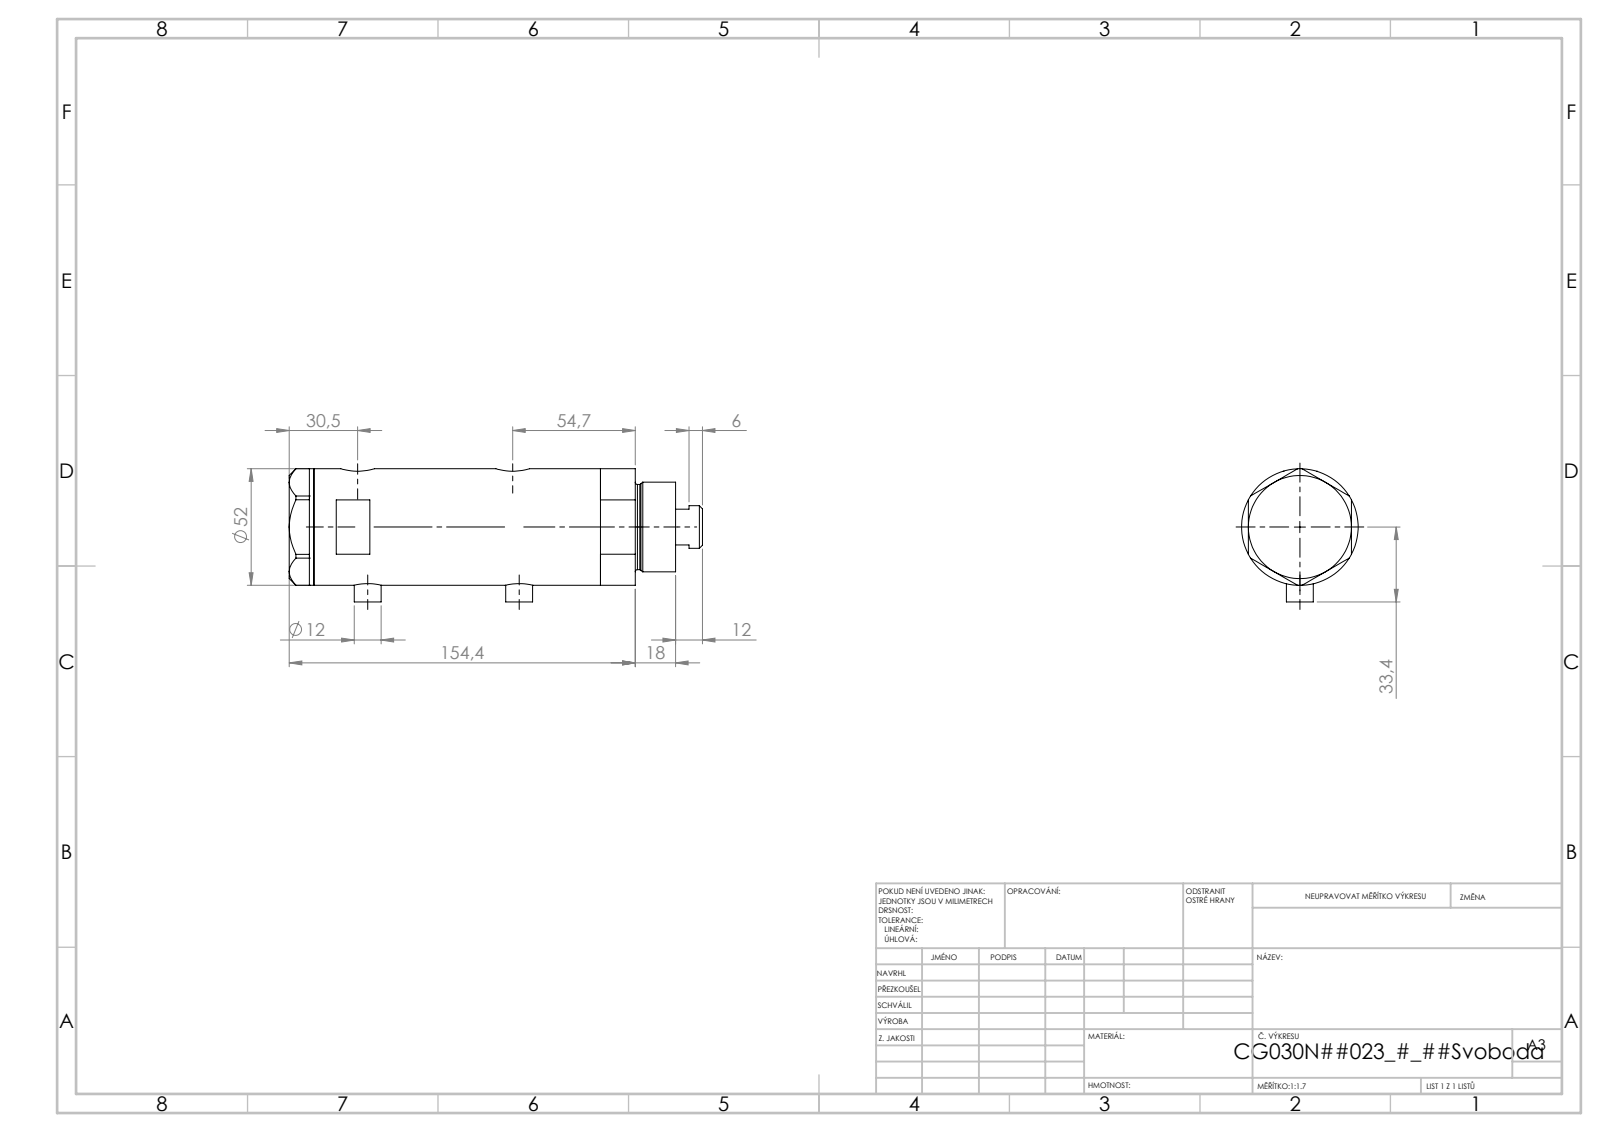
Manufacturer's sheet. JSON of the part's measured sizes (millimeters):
{"part_name": "V270CG_MIDDLE; V270CG_BACK; V270CG_FRONT; V270CG_VC", "step_written_by": "SolidWorks 2019 (CONFIG_CONTROL_DESIGN)", "units": "millimeters", "bodies": {"solids": 4, "faces": 140, "planar": 67, "cylindrical": 53, "other": 20}, "overall_size": [184.4, 59.4, 52], "volume_mm3": 337030, "surface_area_mm2": 77747, "round_holes": [[5, 2], [9.73, 2], [12.5, 2], [15, 2], [6.5, 1], [20, 1], [21.5, 1], [30, 1], [33, 1], [44, 1]], "round_bosses_or_shafts": [[12, 2], [52, 1], [40, 1], [38, 1], [19, 1]], "face_to_face_distances": [91.5, 23.8, 67.7, 11, 34.8, 102.5, 46, 138.9, 127.9, 104.1], "hole_center_spacings": [2.9, 4.5, 64.7, 67.6, 69.2, 72.1]}
